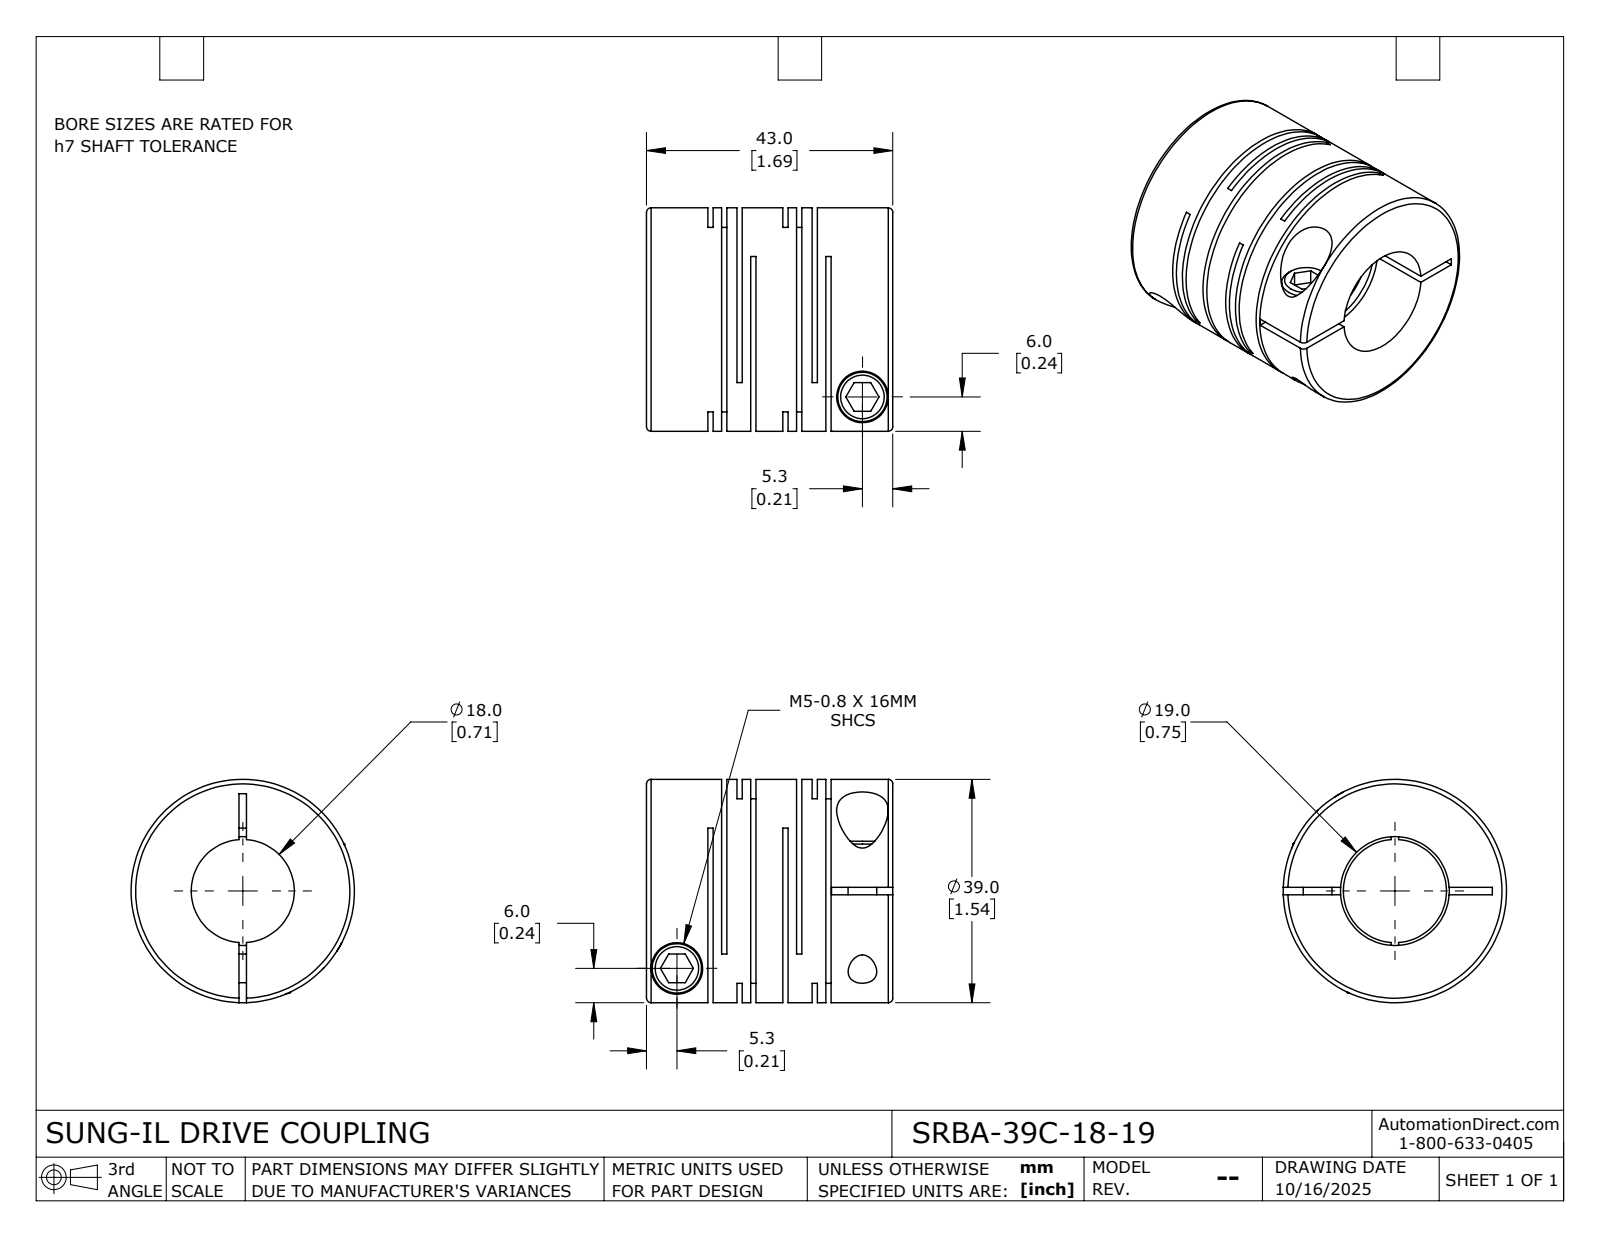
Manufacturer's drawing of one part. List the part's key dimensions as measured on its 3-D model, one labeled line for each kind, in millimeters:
Part name (STEP PRODUCT): SRBA-39C-18-19
STEP written by: SolidWorks 2024 (CONFIG_CONTROL_DESIGN)
Units: millimetres
Bodies: 1 solid, 115 faces (60 planar, 42 cylindrical, 13 other)
Overall size (bounding box): 43 × 39 × 39
Volume: 32 804 mm³ · Surface area: 21 720 mm²
Round holes (diameter × count): ⌀5 ×2, ⌀9 ×2, ⌀18 ×1, ⌀19 ×1
Round bosses / shafts (diameter × count): ⌀8.6 ×2, ⌀39 ×1
Main face-to-face distances: 13.1, 0.92, 2.4, 5.1, 10.7, 14.02, 18.2, 12.18, 3.32, 7.5
